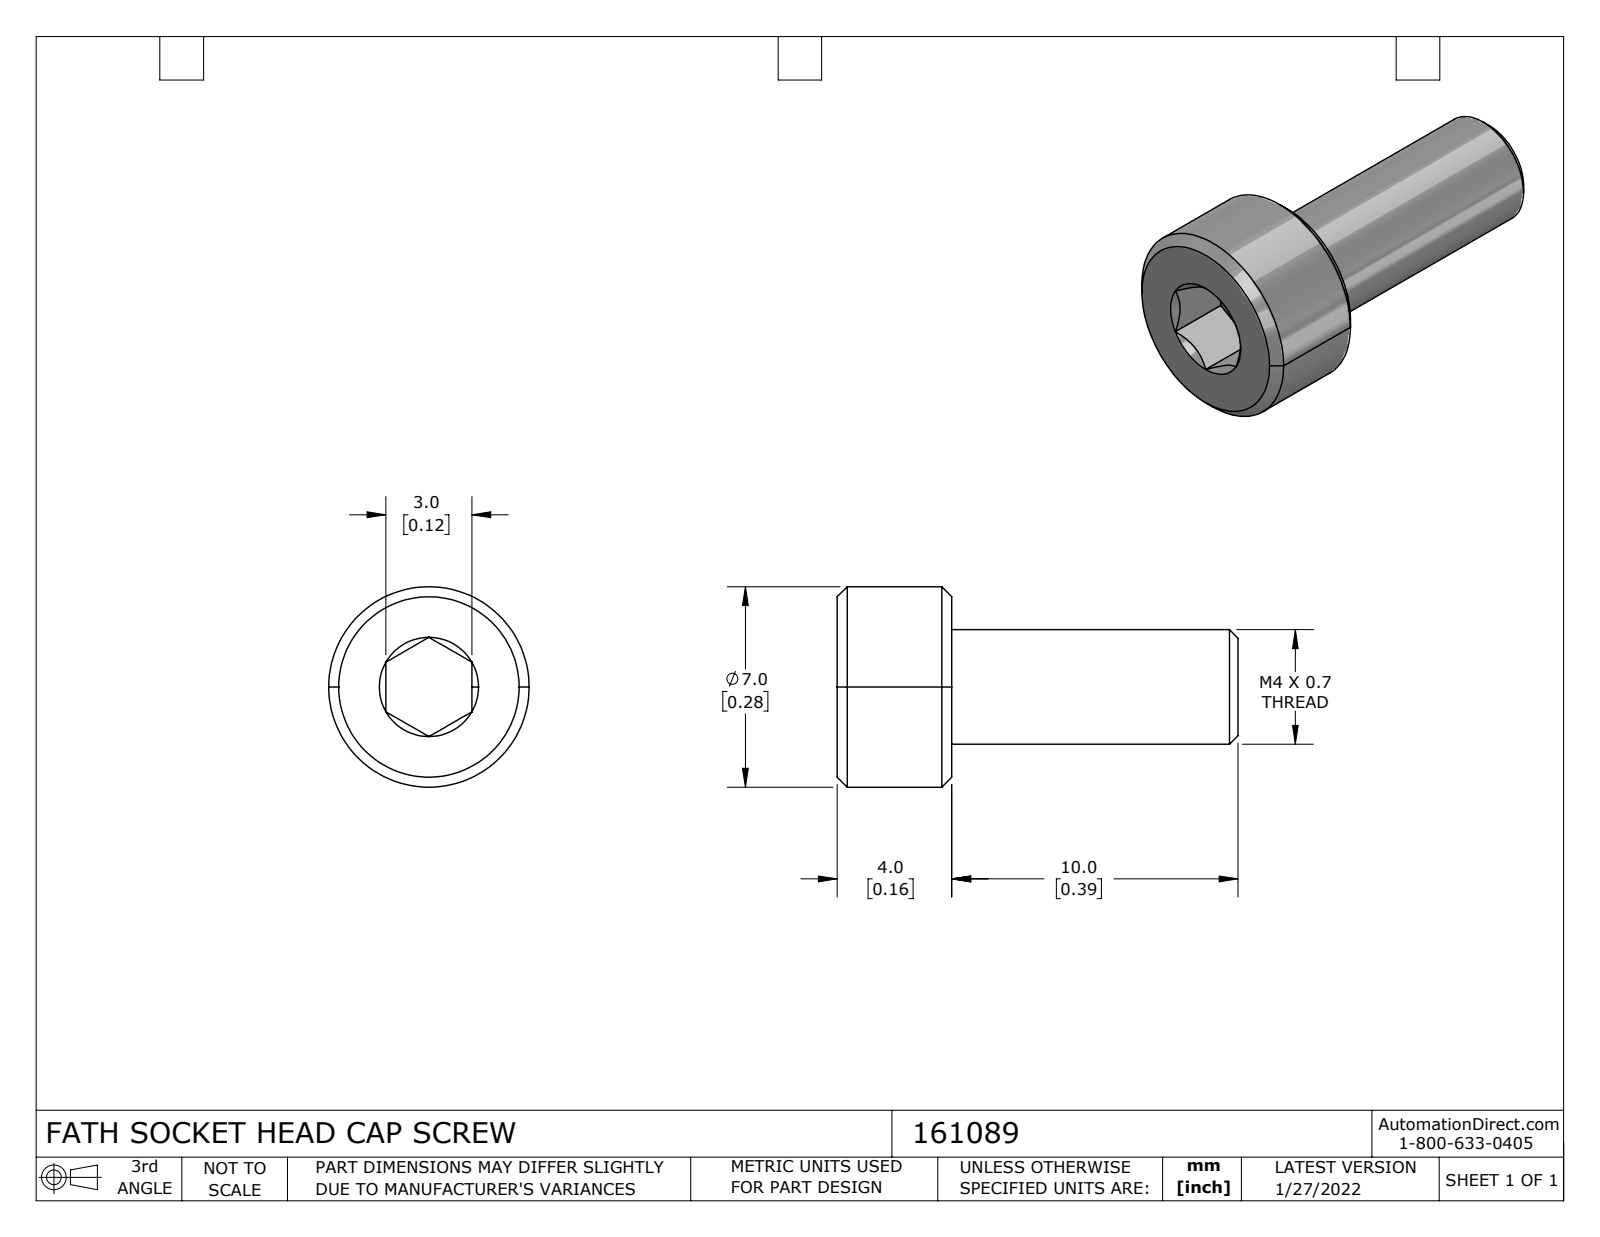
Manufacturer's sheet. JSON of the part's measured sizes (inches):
{"part_name": "161089", "step_written_by": "SolidWorks 2021 (CONFIG_CONTROL_DESIGN)", "units": "inches", "bodies": {"solids": 1, "faces": 27, "planar": 10, "cylindrical": 4, "other": 13}, "overall_size": [0.551, 0.276, 0.276], "volume_in3": 0.016, "surface_area_in2": 0.467, "round_bosses_or_shafts": [[0.276, 1], [0.157, 1]], "face_to_face_distances": [0.157, 0.118, 0.551, 0.394, 0.089, 0.069, 0.463]}
